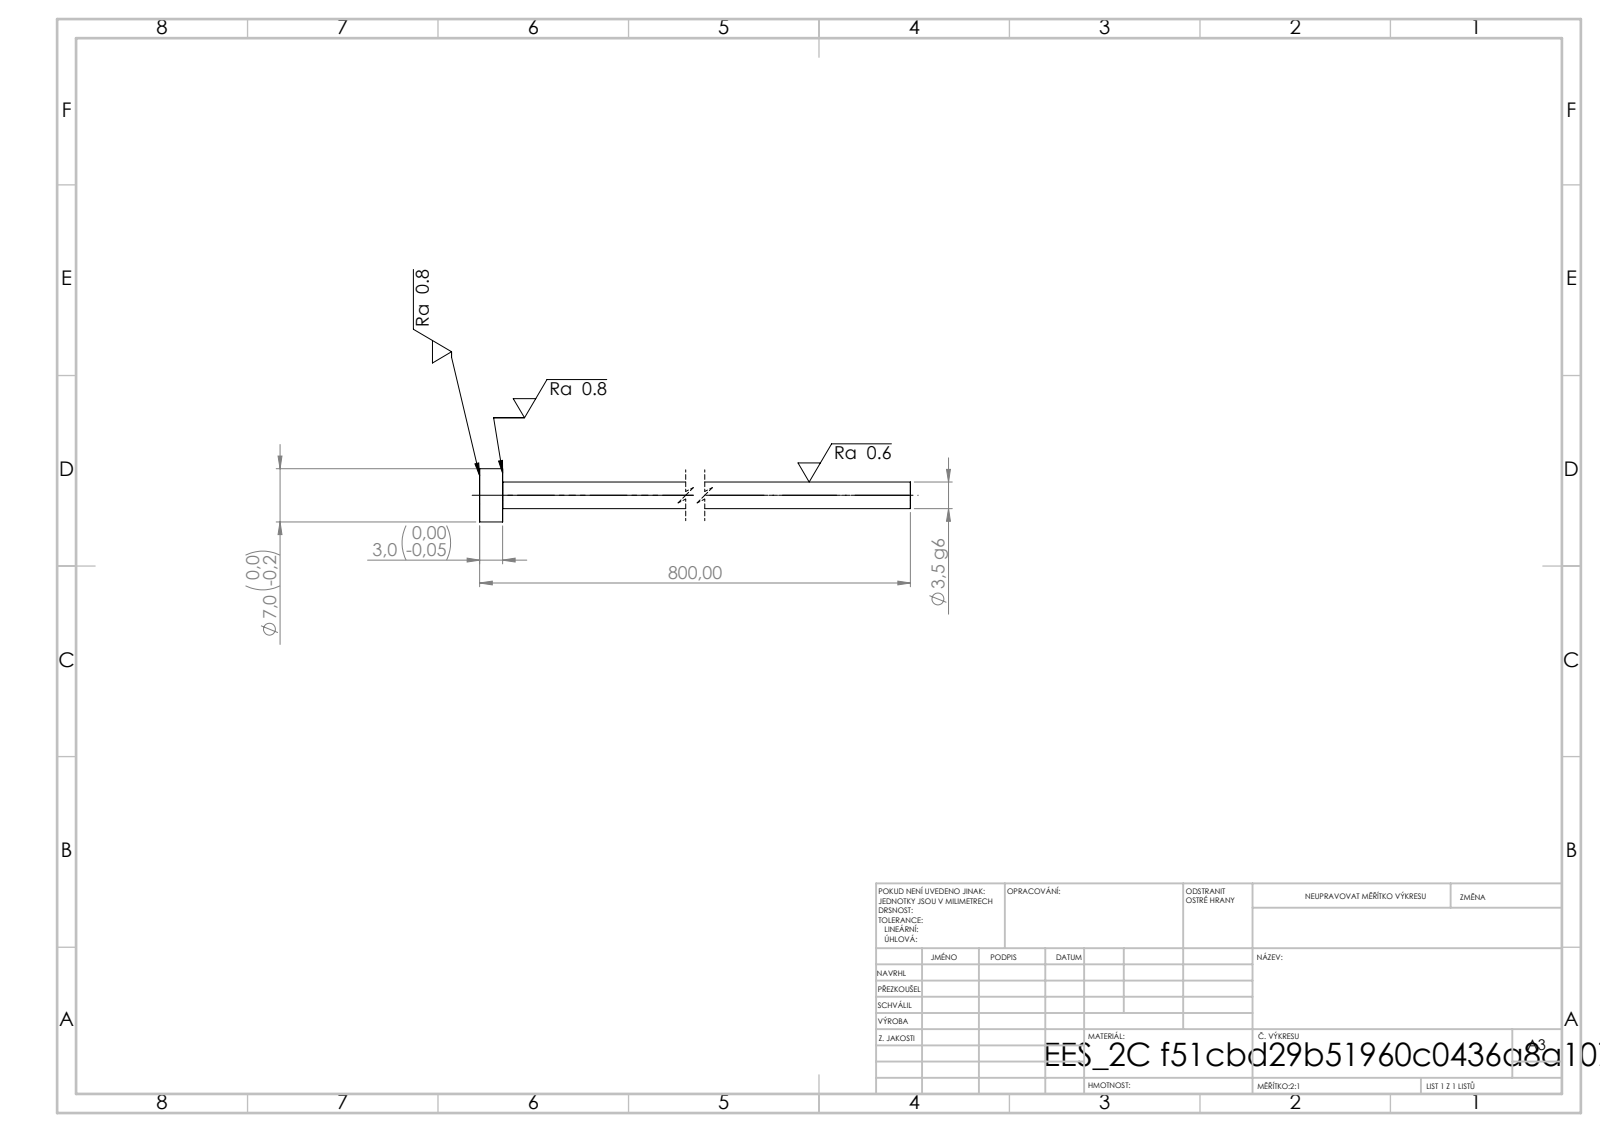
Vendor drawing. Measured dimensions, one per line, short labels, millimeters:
written by: SolidWorks 2019 (CONFIG_CONTROL_DESIGN)
unit: mm
bodies: 1 solid, 7 faces (3 planar, 4 cylindrical, 0 other)
size: 800 × 7 × 7
volume: 7 783 mm³; area: 8 906 mm²
bosses: 1× ⌀7, 1× ⌀3.5
face distances: 3, 800, 797
